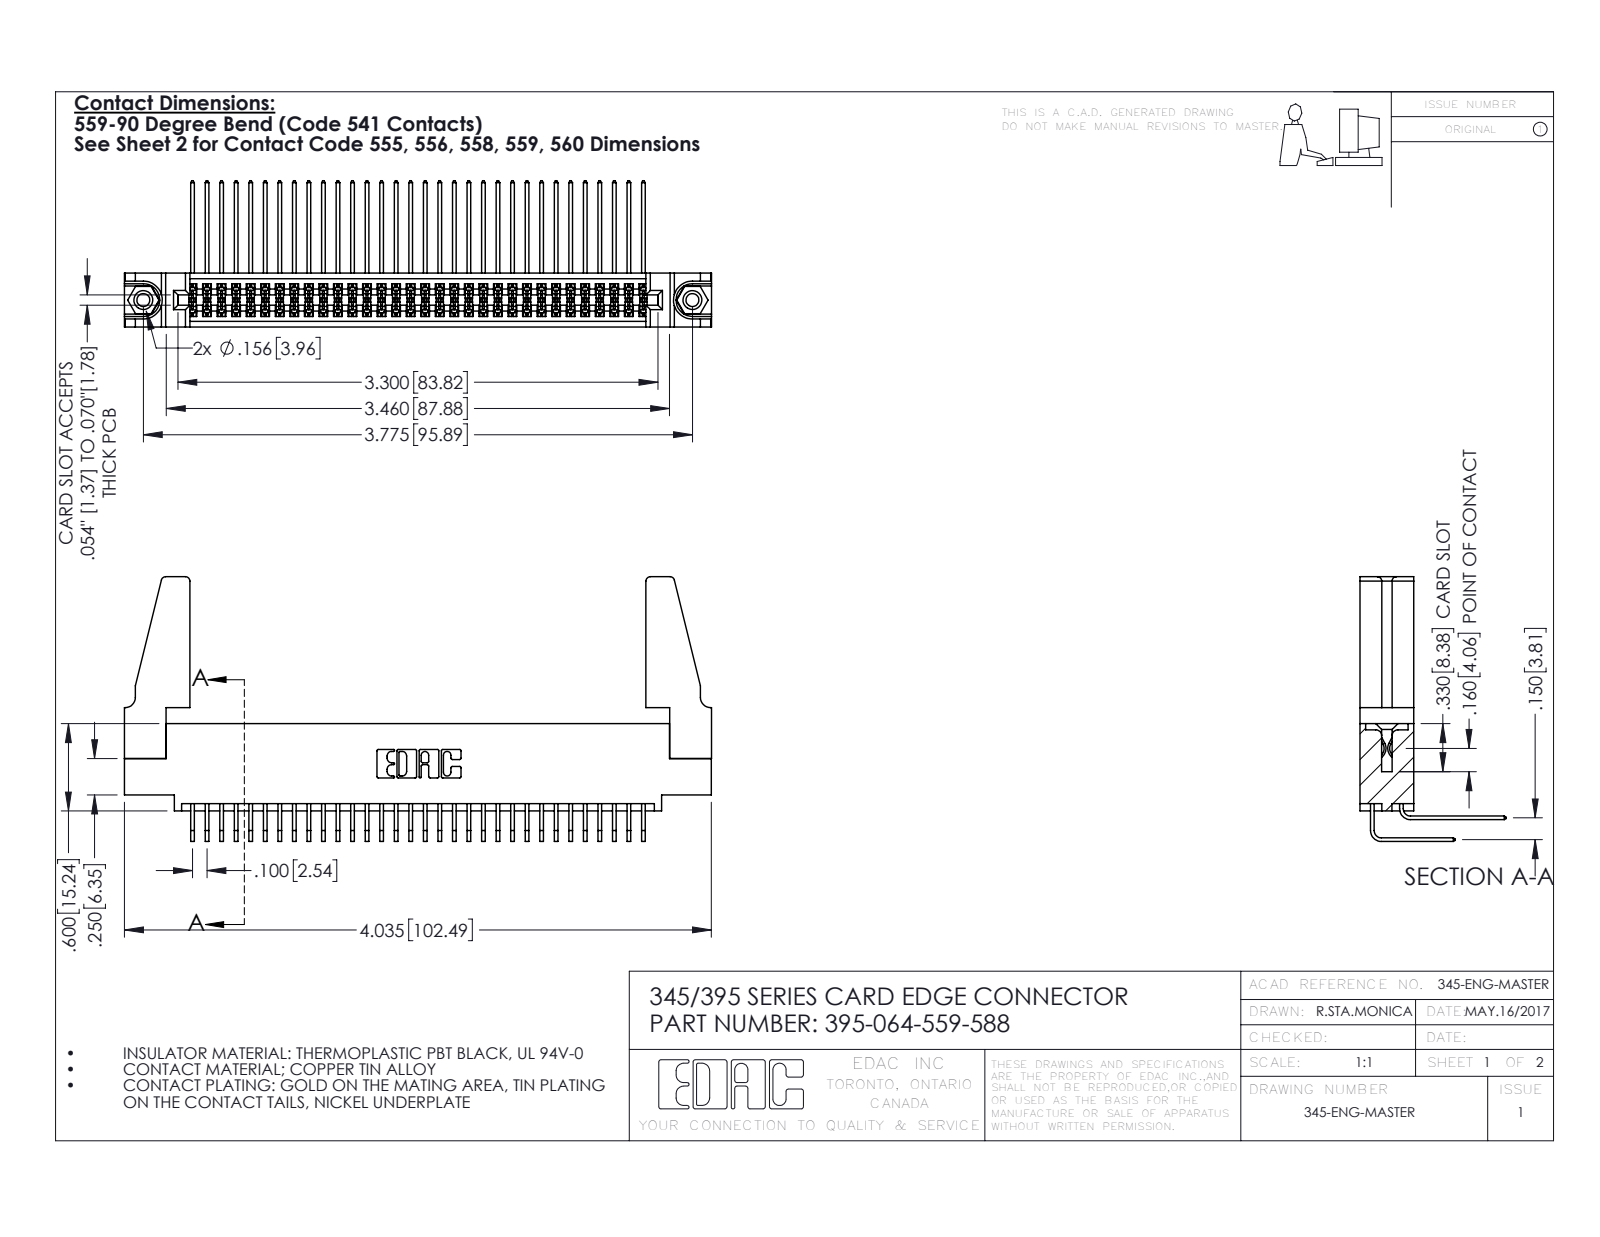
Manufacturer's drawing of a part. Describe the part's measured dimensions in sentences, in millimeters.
The part is named "345-250-001_345-250-001-102; 395-064-559-588; 345-220-078_345-220-088; 345-292-001_559 Tail - 2 (+2 more)". Its 3-D file was written by "SolidWorks 2016 (CONFIG_CONTROL_DESIGN)". It is 69 solids with 3582 faces: 2396 planar, 1170 cylindrical and 16 other. Overall it measures 102.5 by 46.2 by 25.5 millimeters. Its volume is 13 400 cubic millimeters and its surface area 19 780 square millimeters. Round holes: 2 of diameter 2.3, 2 of diameter 3.2, 2 of diameter 4, 1 of diameter 1.6. Round bosses or shafts: 2 of diameter 3.9. Partial cylindrical surfaces (rounded edges, fillets, slot ends): 96 of radius 0.2, 22 of radius 0.3, 8 of radius 0.8, 6 of radius 0.2, 6 of radius 0.8, 3 of radius 0.7, 2 of radius 0.4, 2 of radius 0.5. The main face-to-face distances are 1.8, 7.6, 9.4, 5.1, 2.5, 6.9, 0.6, 5.7, 4.4, 3.8. The hole center spacings are 6.9, 89.9, 95.9.
